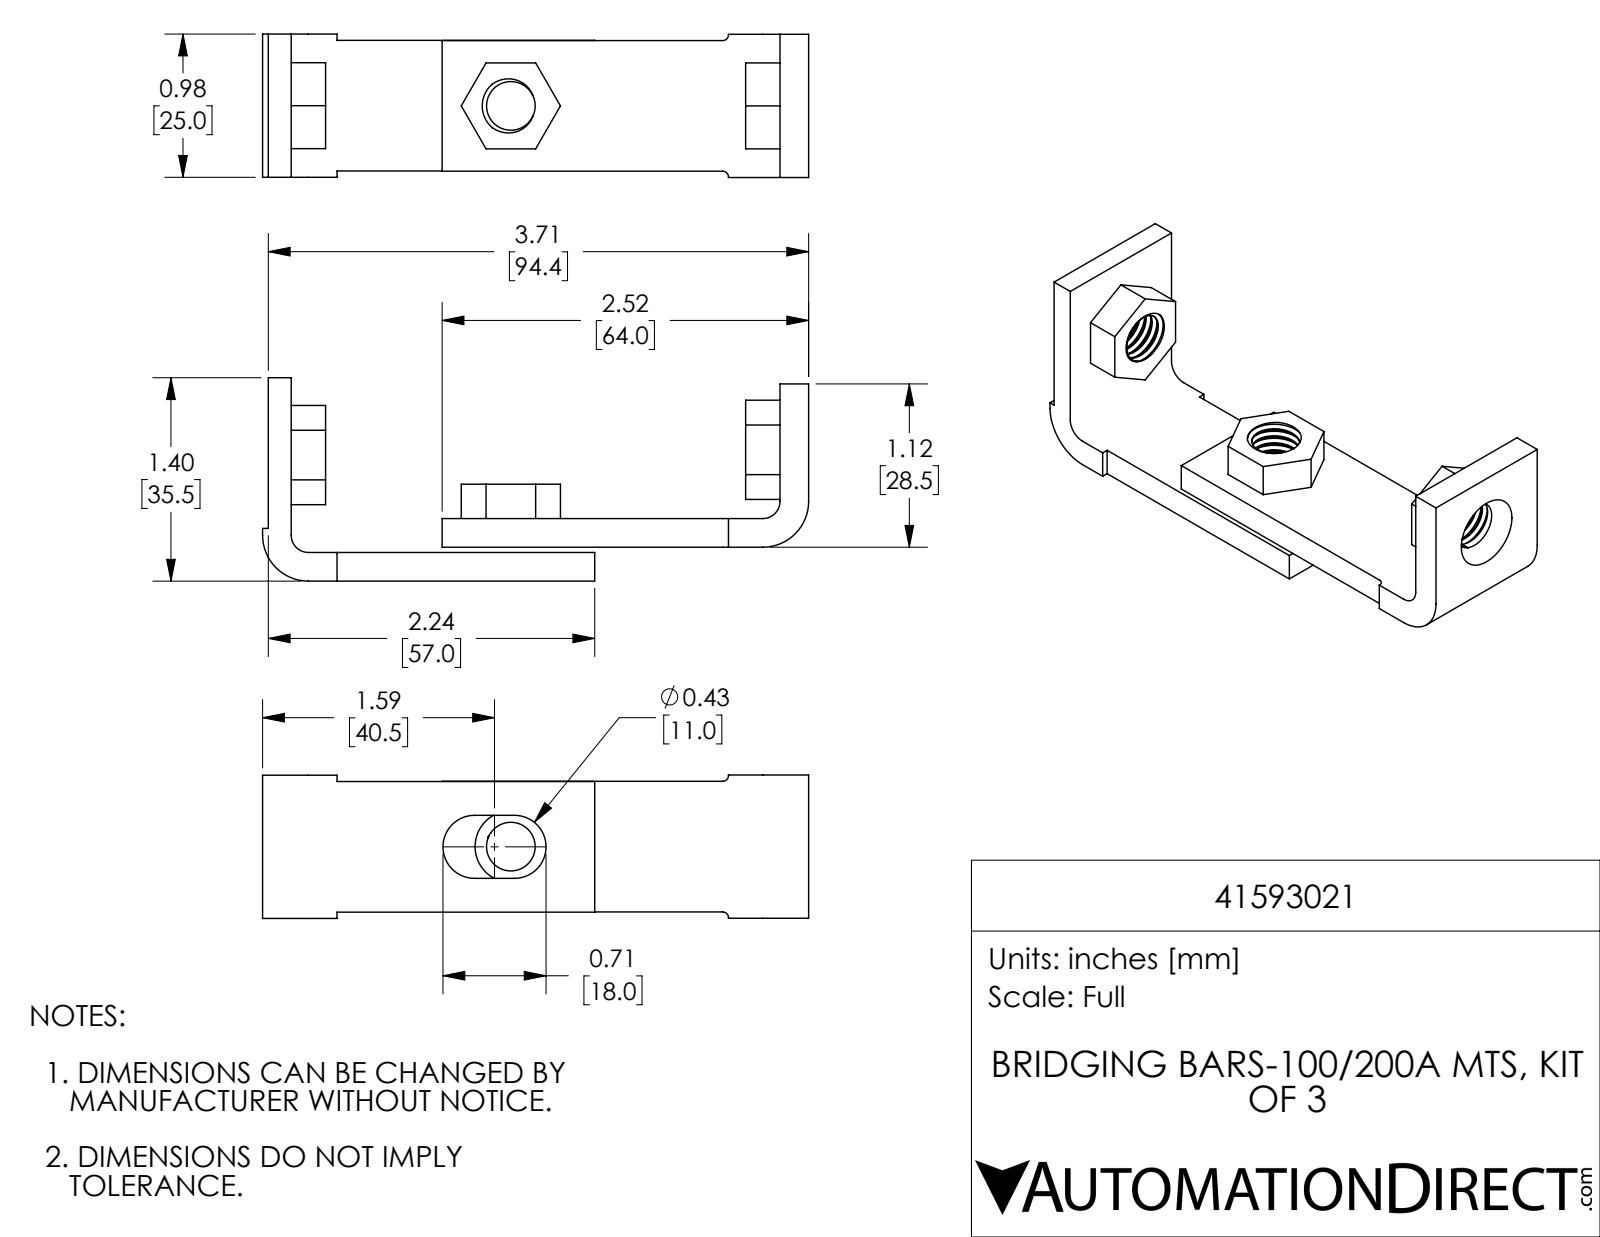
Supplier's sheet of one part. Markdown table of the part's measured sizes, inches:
| quantity | value |
| --- | --- |
| part name | 41593021 |
| STEP written by | SolidWorks 2017 (AUTOMOTIVE_DESIGN) |
| units | inches |
| bodies | 5 solids, 154 faces (58 planar, 90 cylindrical, 6 other) |
| overall size | 3.754 × 1.398 × 0.986 |
| volume | 1.208 in³ |
| surface area | 20.25 in² |
| round holes (diameter × count) | 0.335 × 3, 0.394 × 3, 0.492 × 3 |
| round bosses / shafts (diameter × count) | 0.512 × 3 |
| partial cylindrical surfaces (radius × count) | 0.039 × 2, 0.118 × 2, 0.217 × 2, 0.315 × 2 |
| main face-to-face distances | 0.197, 0.233, 0.43, 0.036, 0.043, 0.941, 0.157, 3.518, 0.898, 0.591 |
| hole center spacings | 0.036 |
